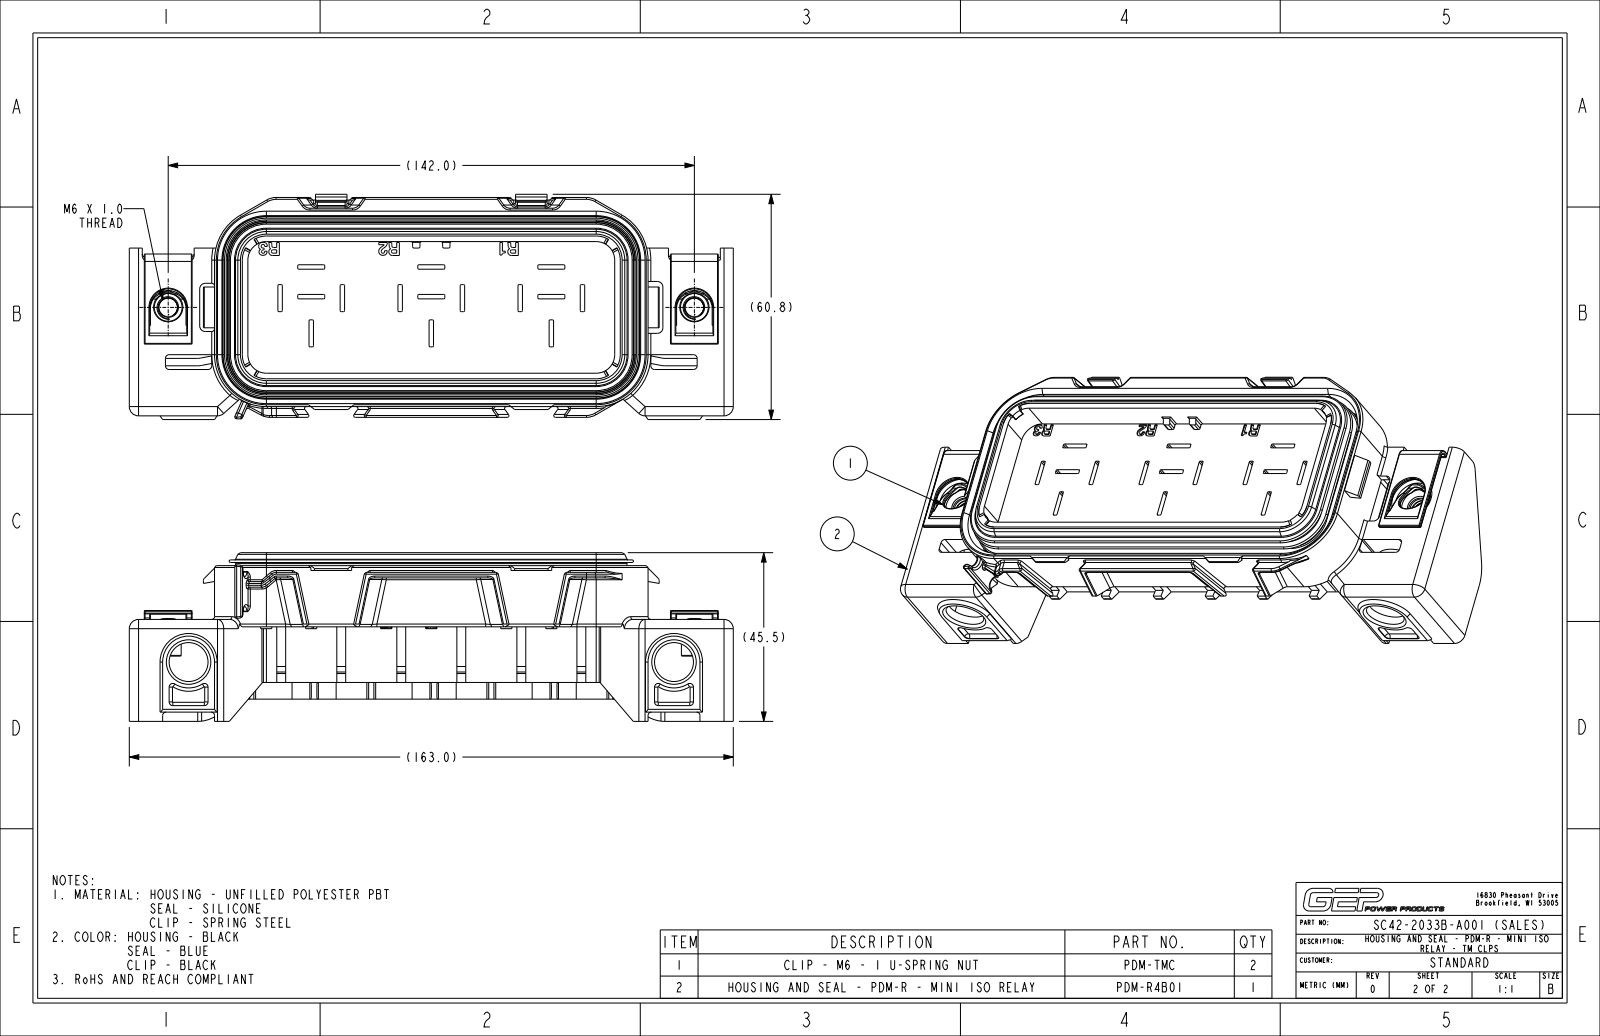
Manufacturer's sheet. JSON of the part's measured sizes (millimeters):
{"part_name": "C26-1012-2B_SALES_NCF; C14-1013_INSTALLED_NCF; PDM-RS_INSTALLED_NCF_ASM; PDM-R4B01_NCF_ASM (+3 more)", "step_written_by": "CREO PARAMETRIC BY PTC INC, 2024014 (CONFIG_CONTROL_DESIGN)", "units": "millimeters", "bodies": {"solids": 4, "faces": 3170, "planar": 1364, "cylindrical": 954, "other": 852}, "overall_size": [163, 60.76, 45.5], "volume_mm3": 102354, "surface_area_mm2": 104060, "round_holes": [[10.5, 4], [5, 2], [7.5, 2], [12.5, 2]], "round_bosses_or_shafts": [[7, 2], [5, 1], [2.5, 1]], "partial_cylinders_radius": [[0.5, 241], [0.3, 106], [0.2, 68], [2, 50], [0.9, 39], [0.45, 38], [4.25, 30], [1, 26]], "face_to_face_distances": [1.5, 2, 11.5, 37, 38.5, 9.5, 7.5, 1.8, 10, 7], "hole_center_spacings": [131, 142]}
